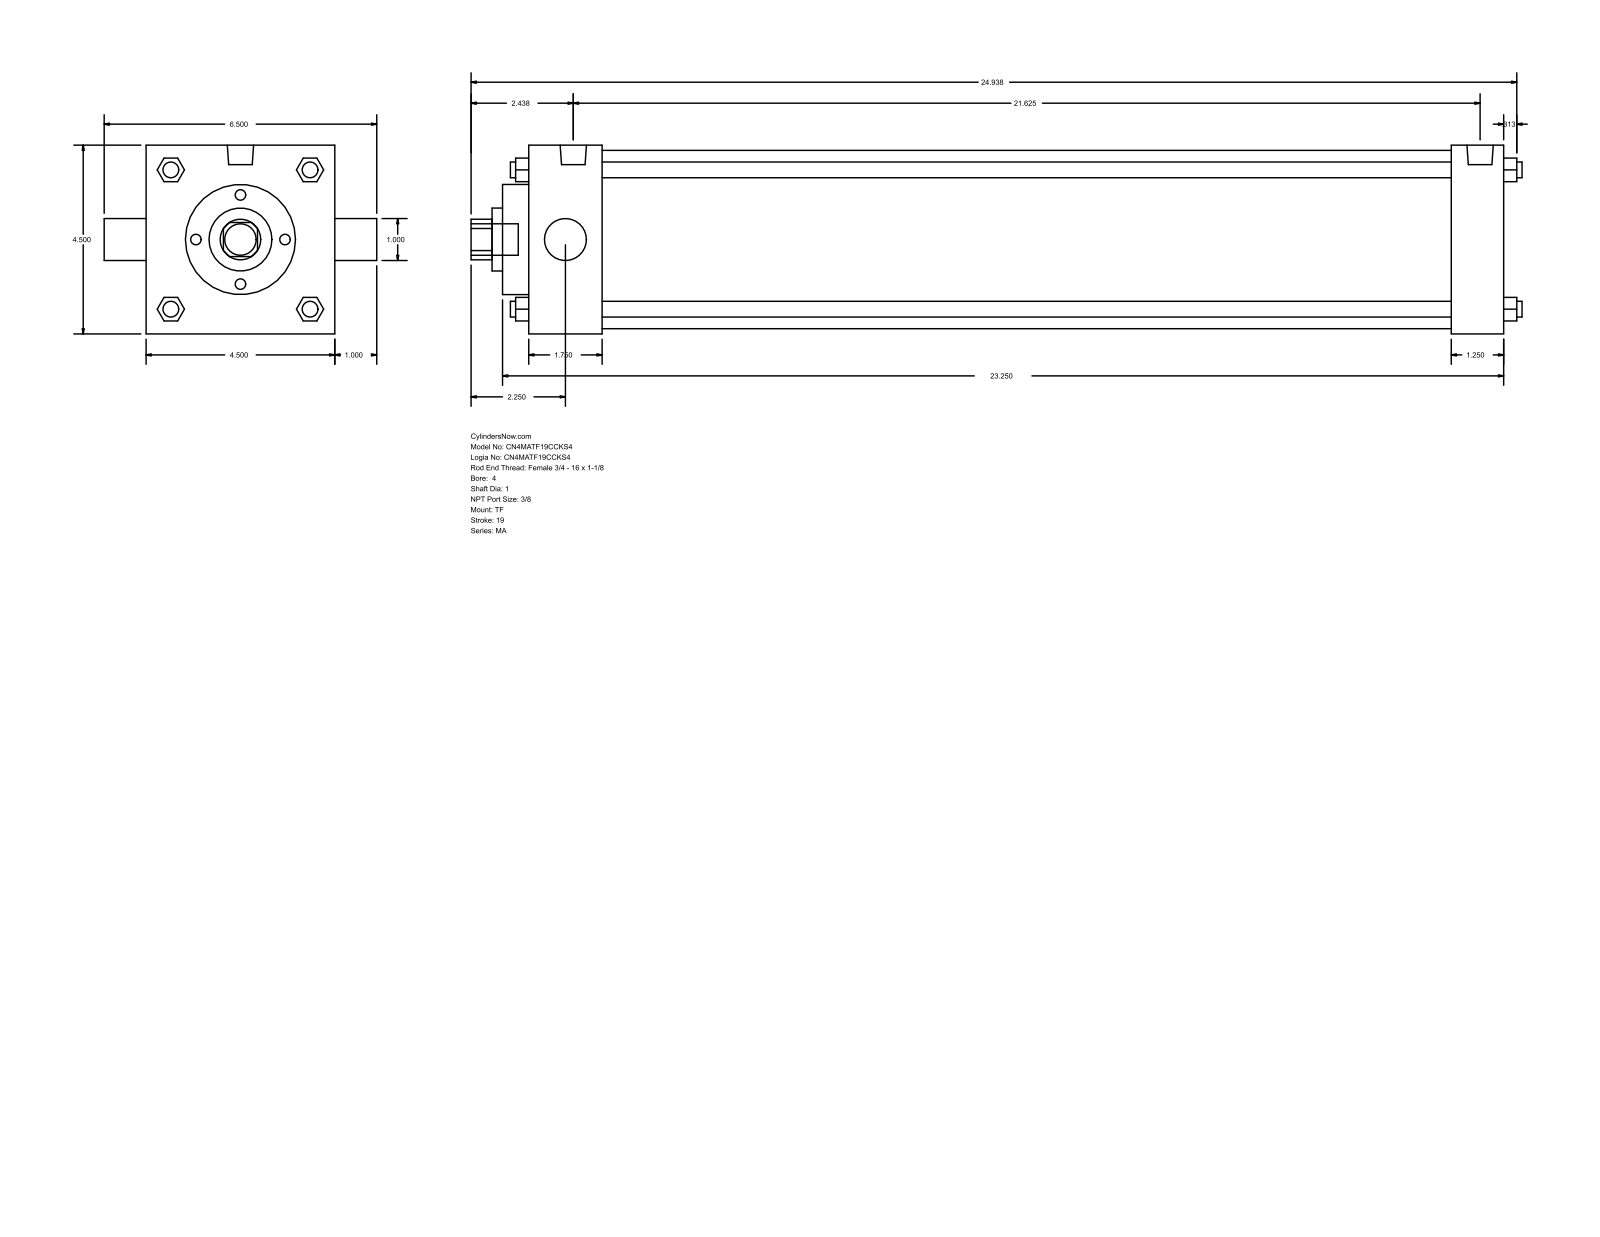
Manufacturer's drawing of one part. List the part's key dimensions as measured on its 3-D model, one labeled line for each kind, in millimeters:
Part name (STEP PRODUCT): MA_TF__0400_1
STEP written by: GSSL Pune (CONFIG_CONTROL_DESIGN)
Units: millimetres
Bodies: 0 solids, 122 faces (93 planar, 29 cylindrical, 0 other)
Overall size (bounding box): 636.59 × 165.1 × 114.3
Round holes (diameter × count): ⌀25.4 ×2, ⌀38.1 ×1, ⌀66.67 ×1, ⌀107.95 ×1
Round bosses / shafts (diameter × count): ⌀9.53 ×4, ⌀11.11 ×3, ⌀15.93 ×2, ⌀19.05 ×1
Partial cylindrical surfaces — rounded edges, fillets, slot ends (radius × count): R12.29 ×1
Main face-to-face distances: 114.3, 590.56, 558.81, 31.75, 44.46, 514.35, 546.1, 15.87, 60.33, 574.68
